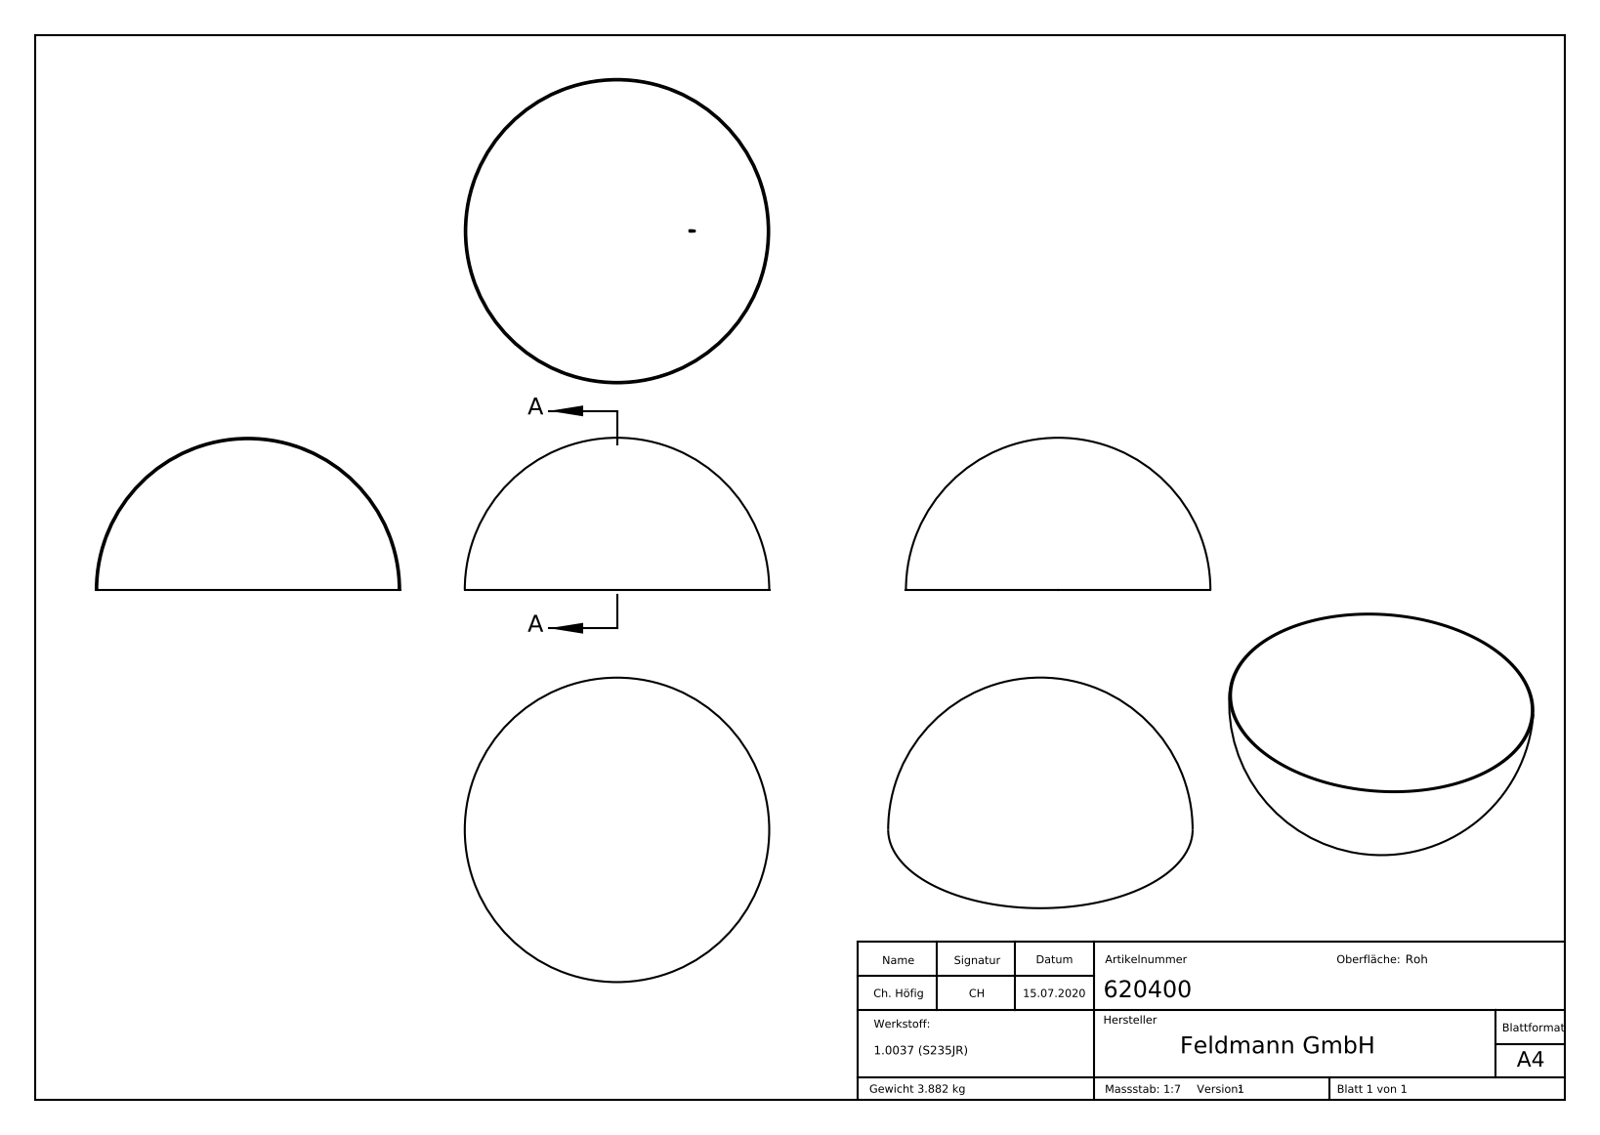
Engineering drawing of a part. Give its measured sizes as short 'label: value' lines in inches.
name: 620400
written by: SolidWorks 2018 (CONFIG_CONTROL_DESIGN)
unit: in
bodies: 1 solid, 191 faces (77 planar, 0 cylindrical, 114 other)
size: 15.748 × 15.748 × 7.874
volume: 30.37 in³; area: 775.2 in²
face distances: 0.047, 0.022, 0.02, 0.032, 0.172, 0.026, 0.153, 0.069, 0.204, 0.052
